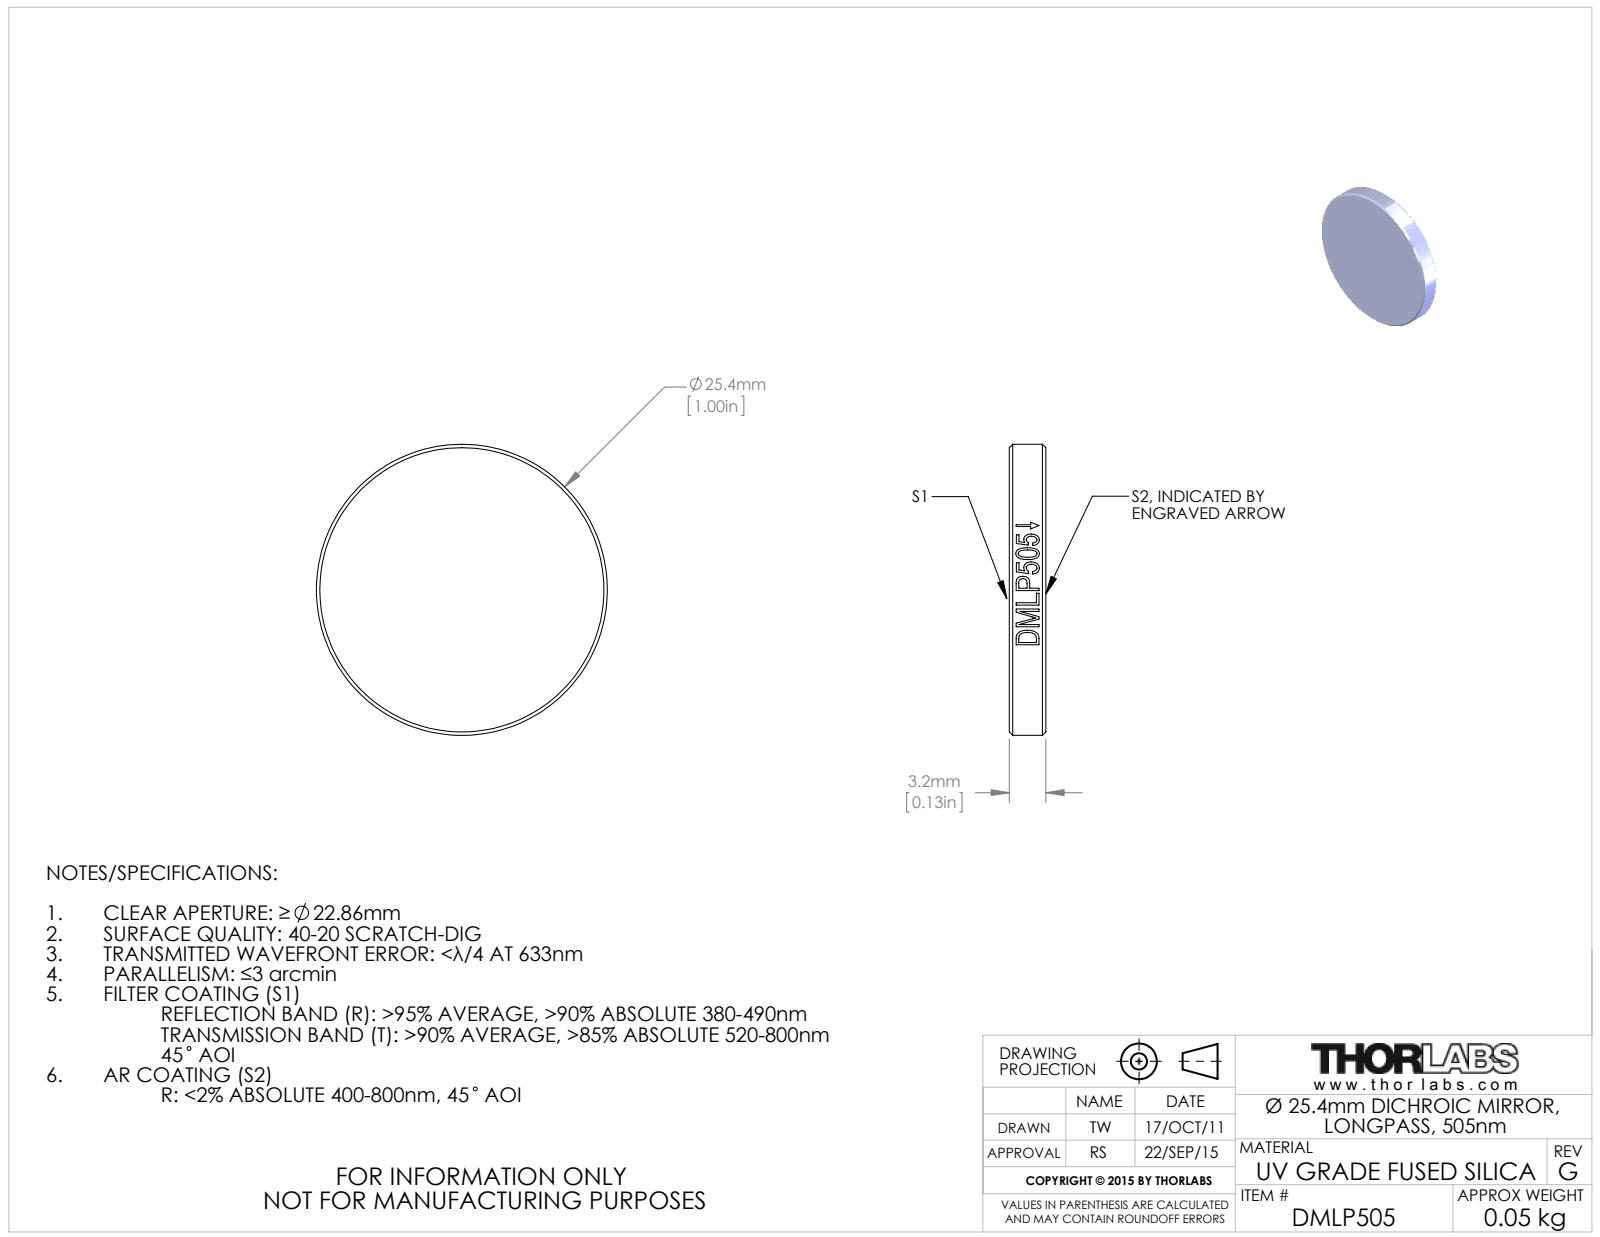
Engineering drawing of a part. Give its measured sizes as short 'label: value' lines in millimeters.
name: 18095-E0W
written by: SolidWorks 2011 (CONFIG_CONTROL_DESIGN)
unit: mm
bodies: 0 solids, 19 faces (2 planar, 13 cylindrical, 4 other)
size: 25.4 × 25.4 × 3.2
bosses: 1× ⌀25.4
face distances: 3.2
